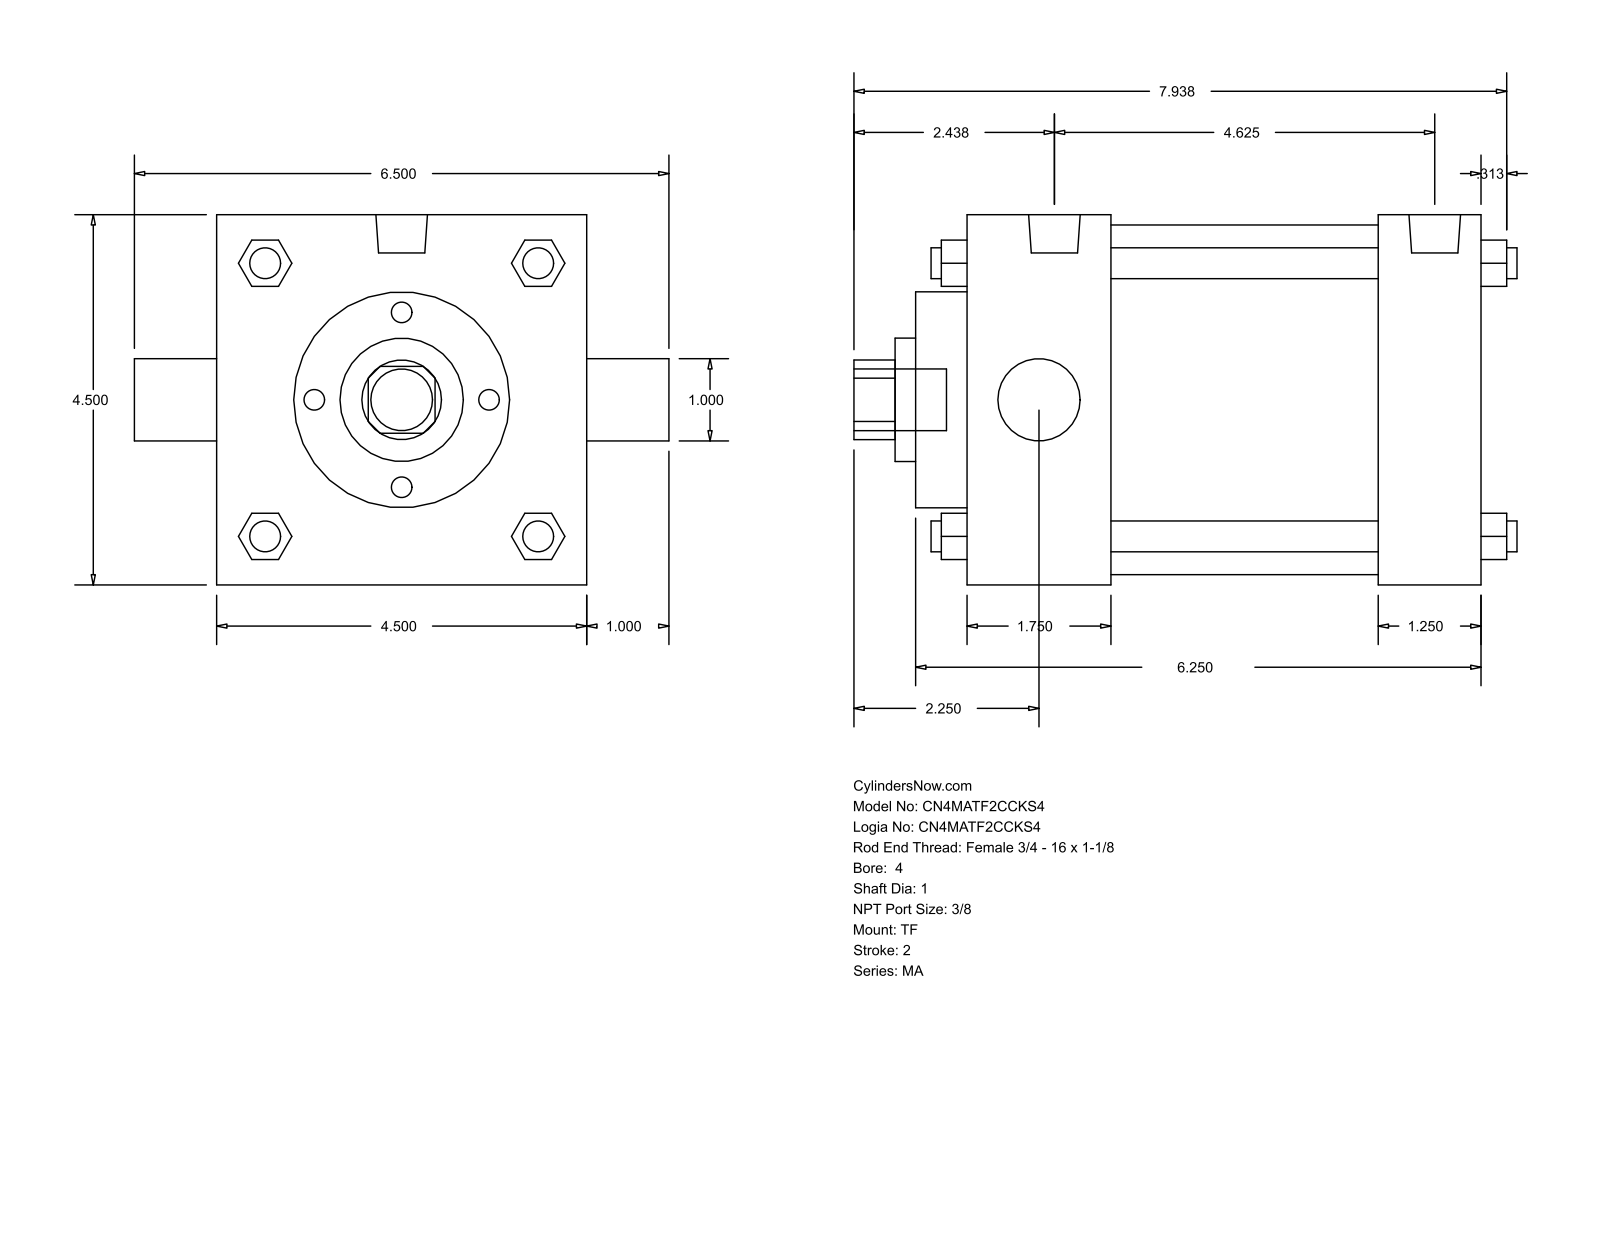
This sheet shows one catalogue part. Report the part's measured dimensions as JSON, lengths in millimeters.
{"part_name": "MA_TF__0400_1", "step_written_by": "GSSL Pune (CONFIG_CONTROL_DESIGN)", "units": "millimeters", "bodies": {"solids": 0, "faces": 122, "planar": 93, "cylindrical": 29, "other": 0}, "overall_size": [204.79, 165.1, 114.3], "round_holes": [[25.4, 2], [38.1, 1], [66.67, 1], [107.95, 1]], "round_bosses_or_shafts": [[9.53, 4], [11.11, 3], [15.93, 2], [19.05, 1]], "partial_cylinders_radius": [[12.29, 1]], "face_to_face_distances": [114.3, 158.76, 127.01, 31.75, 44.46, 82.55, 15.87, 60.33, 142.88, 174.63]}
